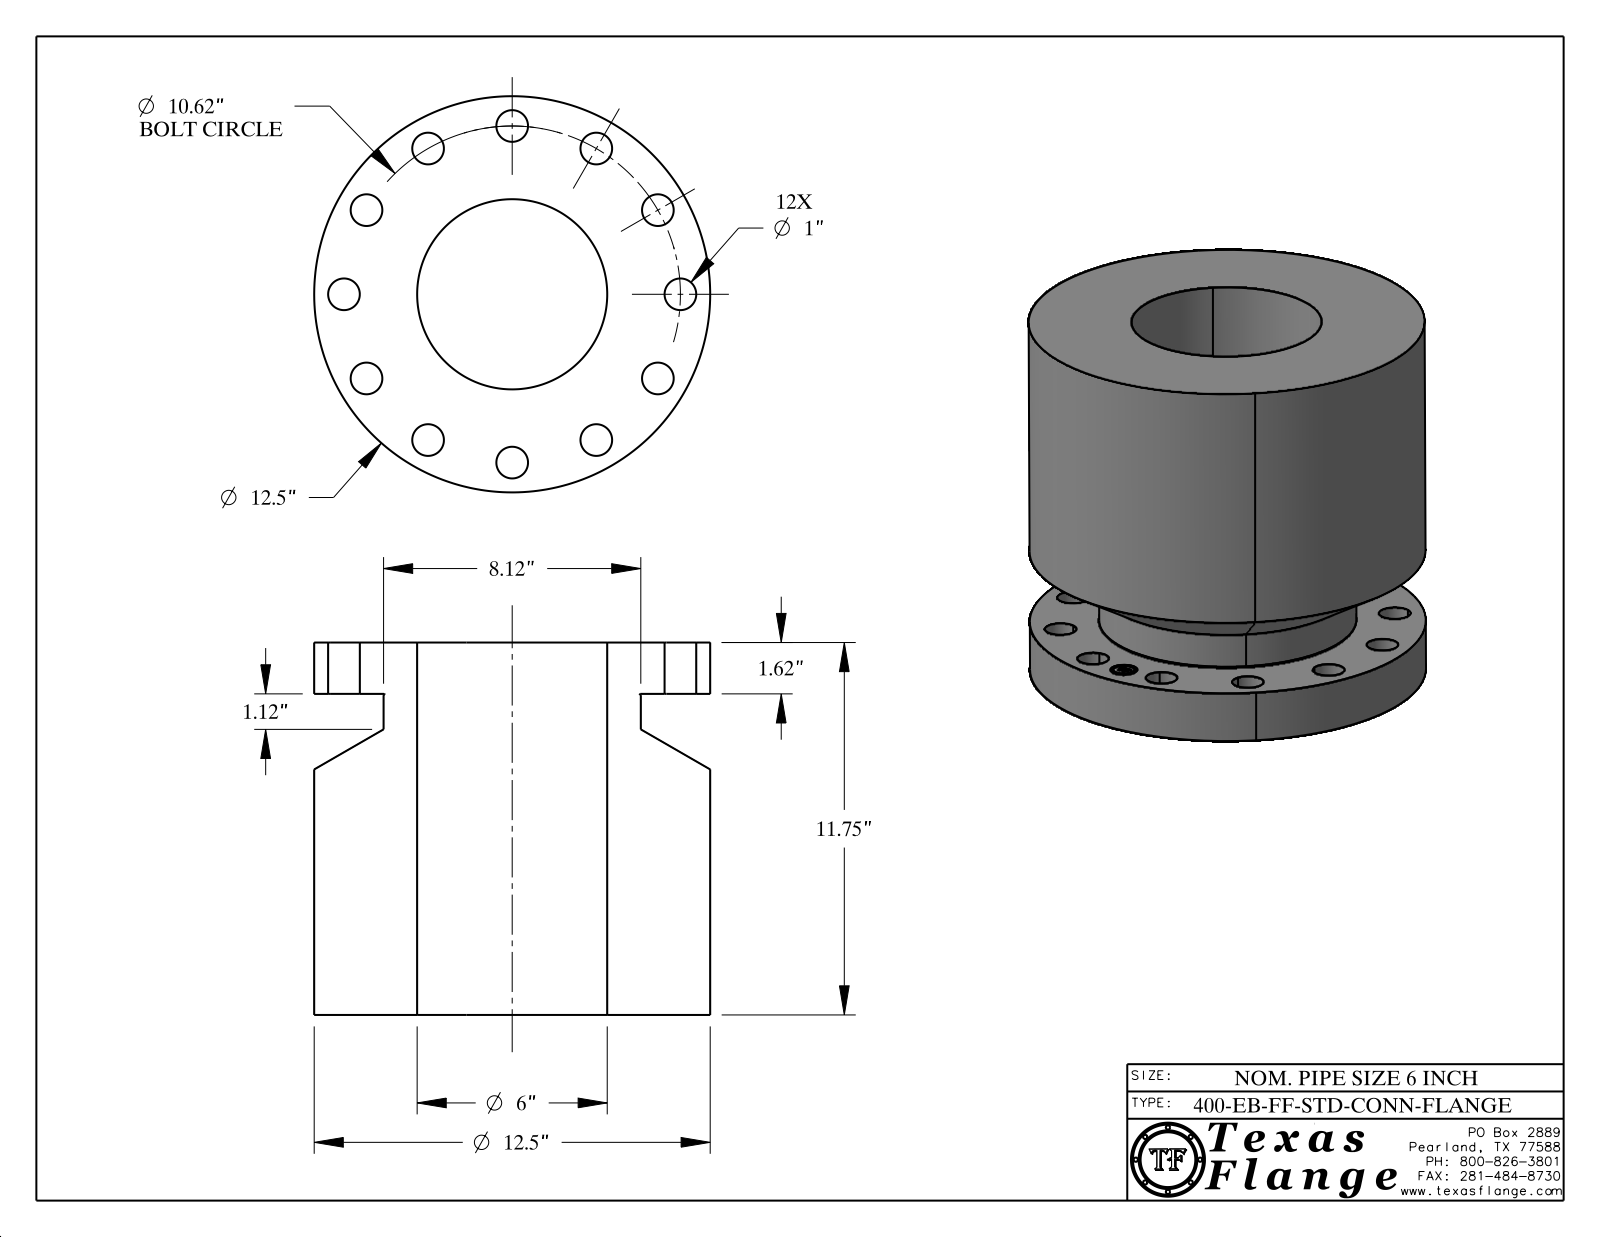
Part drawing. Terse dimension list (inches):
name: 6-400-EB-FF-STD-CONN-FLANGE
written by: CATIA V5 STEP AP214 (AUTOMOTIVE_DESIGN)
unit: in
bodies: 1 solid, 426 faces (368 planar, 52 cylindrical, 6 other)
size: 12.5 × 12.5 × 11.75
volume: 967 in³; area: 1 003 in²
holes: 12× ⌀1, 1× ⌀0.85, 1× ⌀6
bosses: 8× ⌀0.051, 1× ⌀12.5, 1× ⌀8.12, 1× ⌀0.67
face distances: 11.75, 1.62, 10.13, 1.615, 10.135, 0.254, 0.248, 0.016, 0.046, 0.165
hole spacings: 5.31, 10.258, 2.749, 7.509, 9.197, 10.62, 5.31, 2.748
